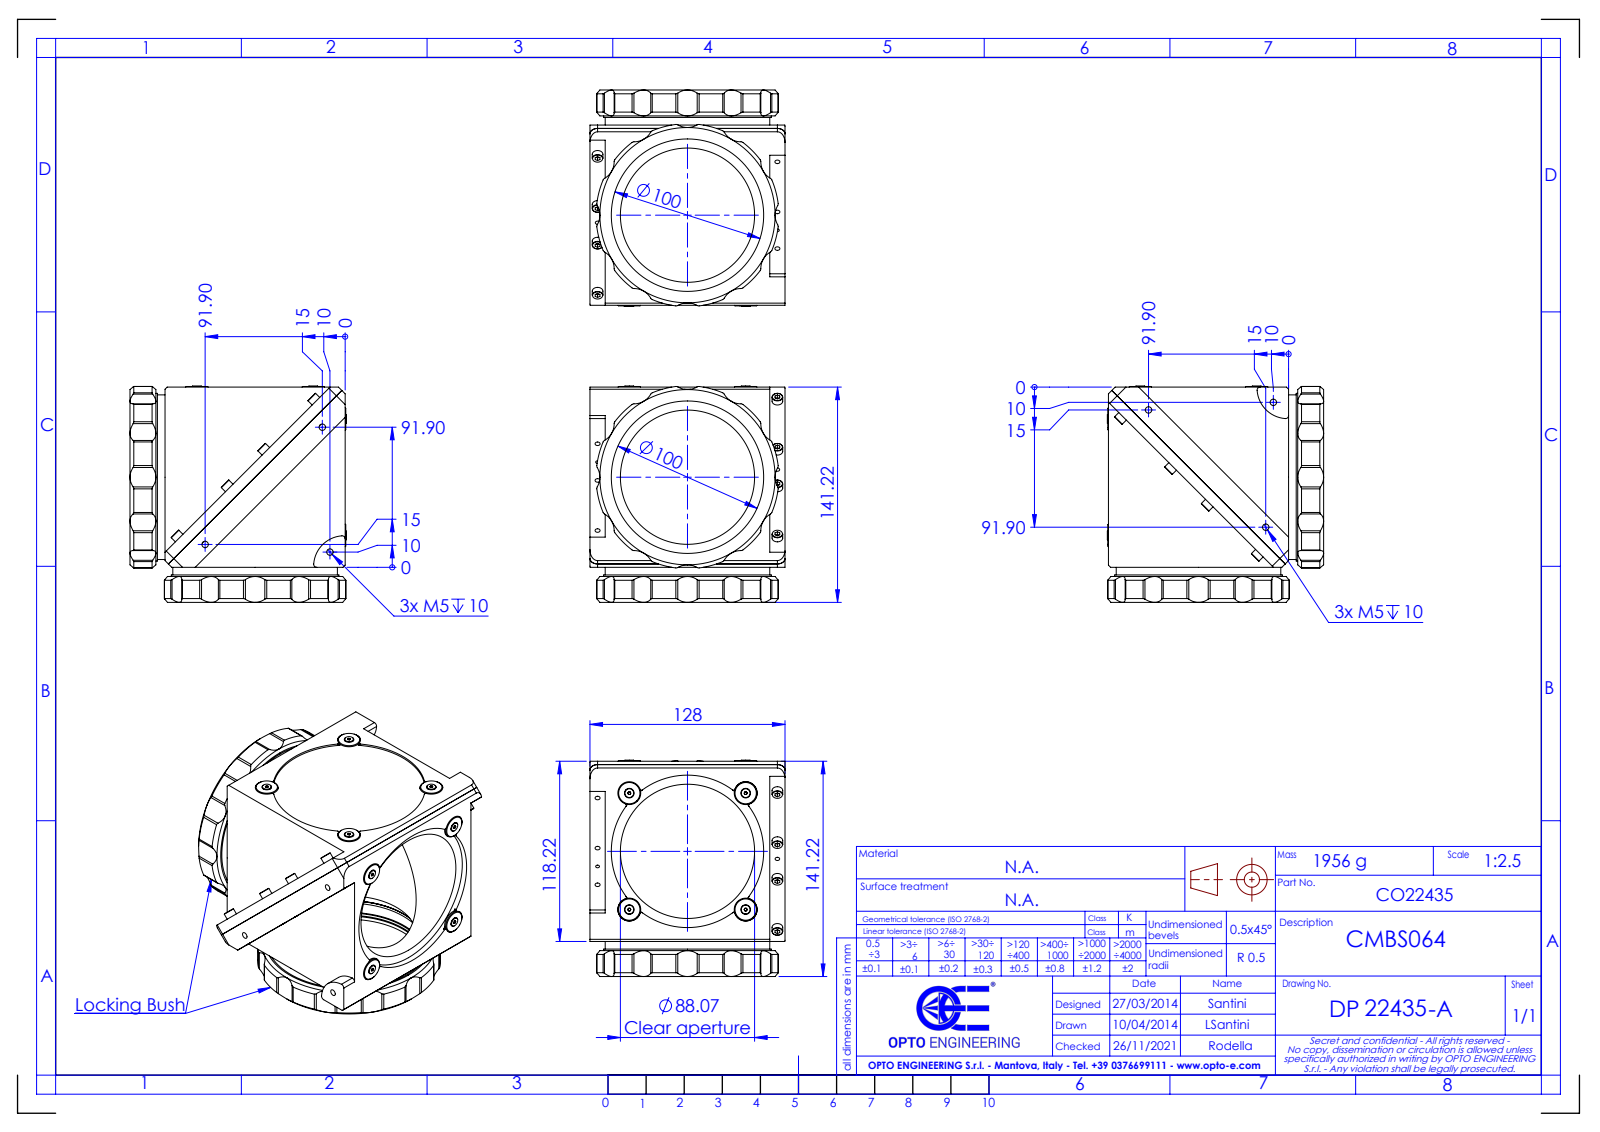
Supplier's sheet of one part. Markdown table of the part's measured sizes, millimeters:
| quantity | value |
| --- | --- |
| part name | DP22435 -A_CMBS064 |
| STEP written by | SolidWorks 2021 (CONFIG_CONTROL_DESIGN) |
| units | millimeters |
| bodies | 0 solids, 585 faces (153 planar, 296 cylindrical, 136 other) |
| overall size | 141.94 × 141.94 × 128 |
| round holes (diameter × count) | 3.3 × 8, 4.2 × 6, 15 × 4, 2.5 × 2, 3 × 2, 88.07 × 2, 100 × 2, 100.6 × 2, 102.2 × 2, 104 × 2, 108 × 2 |
| round bosses / shafts (diameter × count) | 7 × 8, 5.75 × 8, 15 × 4, 110 × 2 |
| partial cylindrical surfaces (radius × count) | 2 × 52, 12.5 × 24, 1 × 16, 5 × 4, 20 × 2, 60 × 2 |
| main face-to-face distances | 2, 108, 3, 10, 118.22, 118, 114.22, 7, 4, 1 |
| hole center spacings | 118, 17, 46.47, 53.99, 63.47, 80.47, 82.05, 94.64 |
